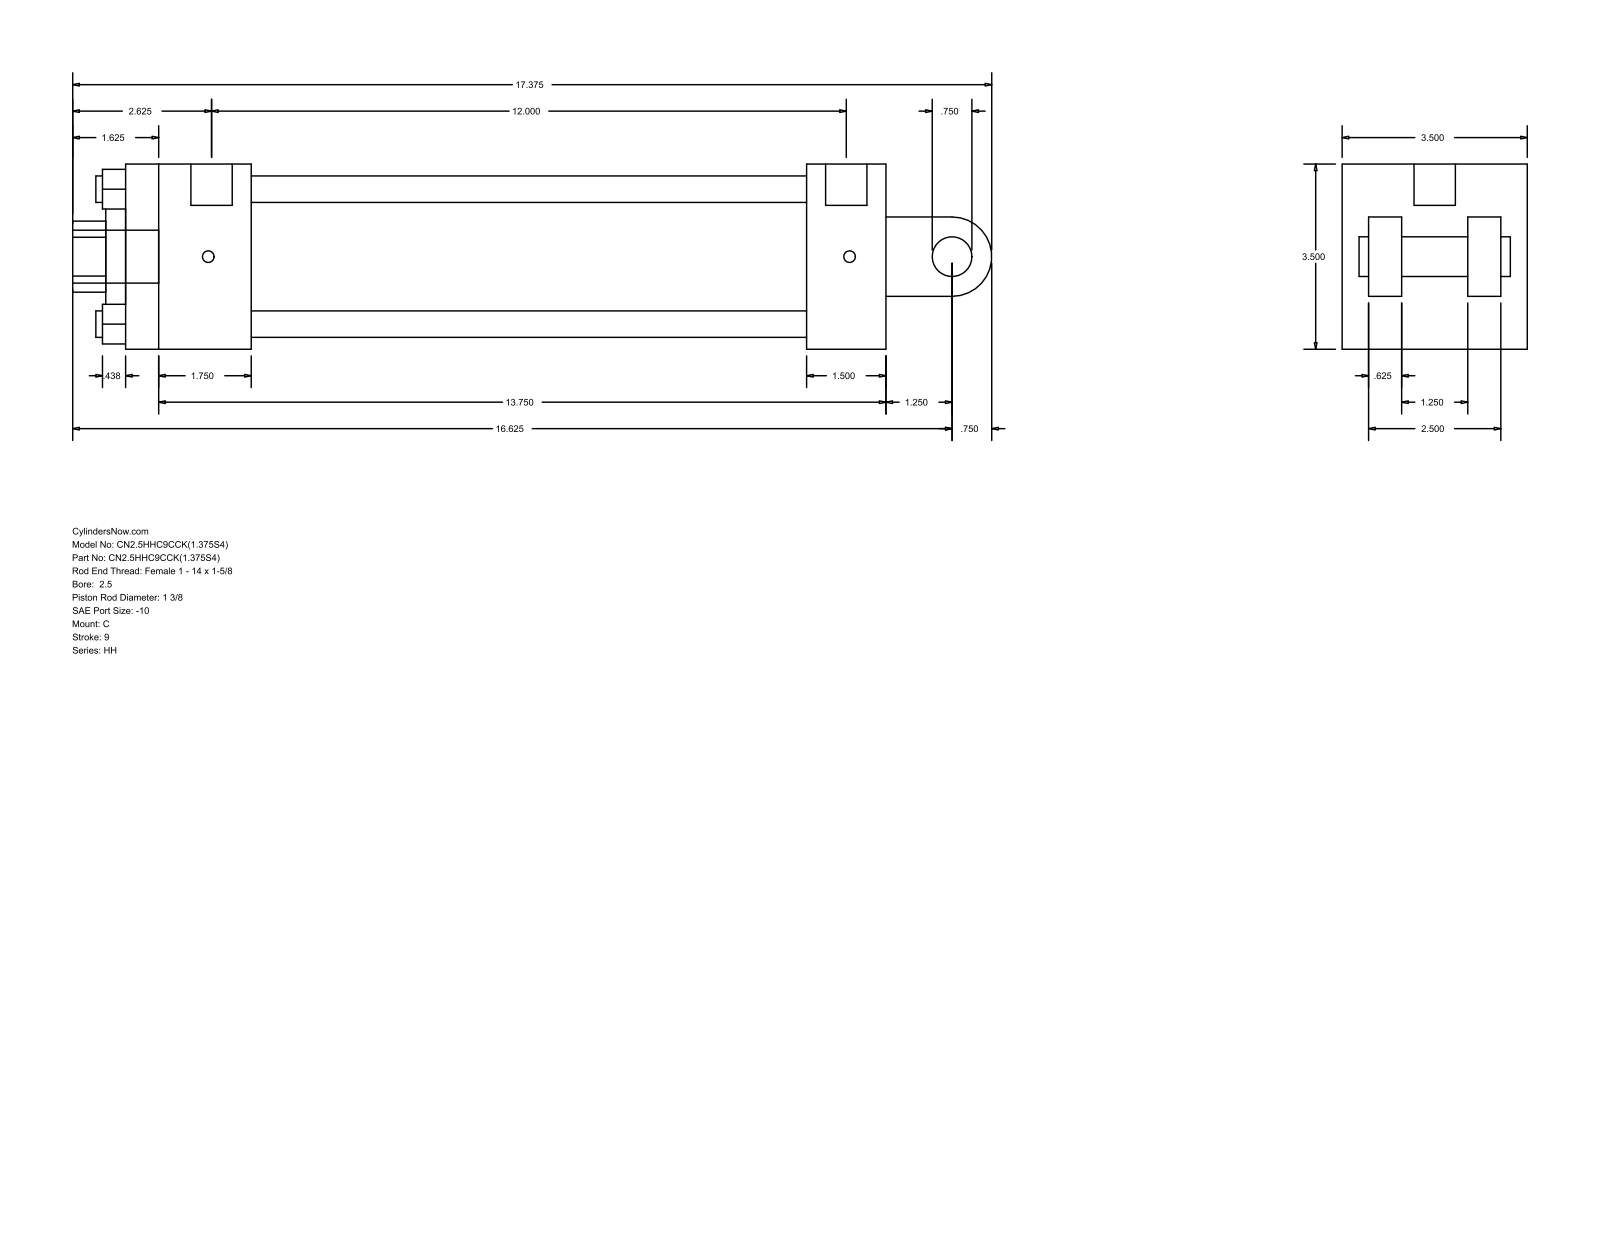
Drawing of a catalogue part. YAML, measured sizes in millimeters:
part_name: "HH_C__0250_1.375"
step_written_by: "GSSL Pune (CONFIG_CONTROL_DESIGN)"
units: millimeters
bodies: {solids: 0, faces: 99, planar: 70, cylindrical: 29, other: 0}
overall_size: [441.32, 88.9, 88.9]
round_holes:
  - {diameter: 12.7, count: 4}
  - {diameter: 5.56, count: 2}
  - {diameter: 19.84, count: 1}
  - {diameter: 34.92, count: 1}
  - {diameter: 50.8, count: 1}
  - {diameter: 73.03, count: 1}
round_bosses_or_shafts:
  - {diameter: 5.56, count: 2}
  - {diameter: 25.4, count: 1}
  - {diameter: 19.84, count: 1}
  - {diameter: 19.05, count: 1}
partial_cylinders:
  - {radius: 17.06, count: 1}
  - {radius: 19.05, count: 1}
face_to_face_distances: [88.9, 365.12, 63.5, 15.87, 12.7, 327.03, 38.09, 60.32, 266.71, 304.8]
hole_center_spacings: [45.79, 64.76, 91.58, 1.58]
